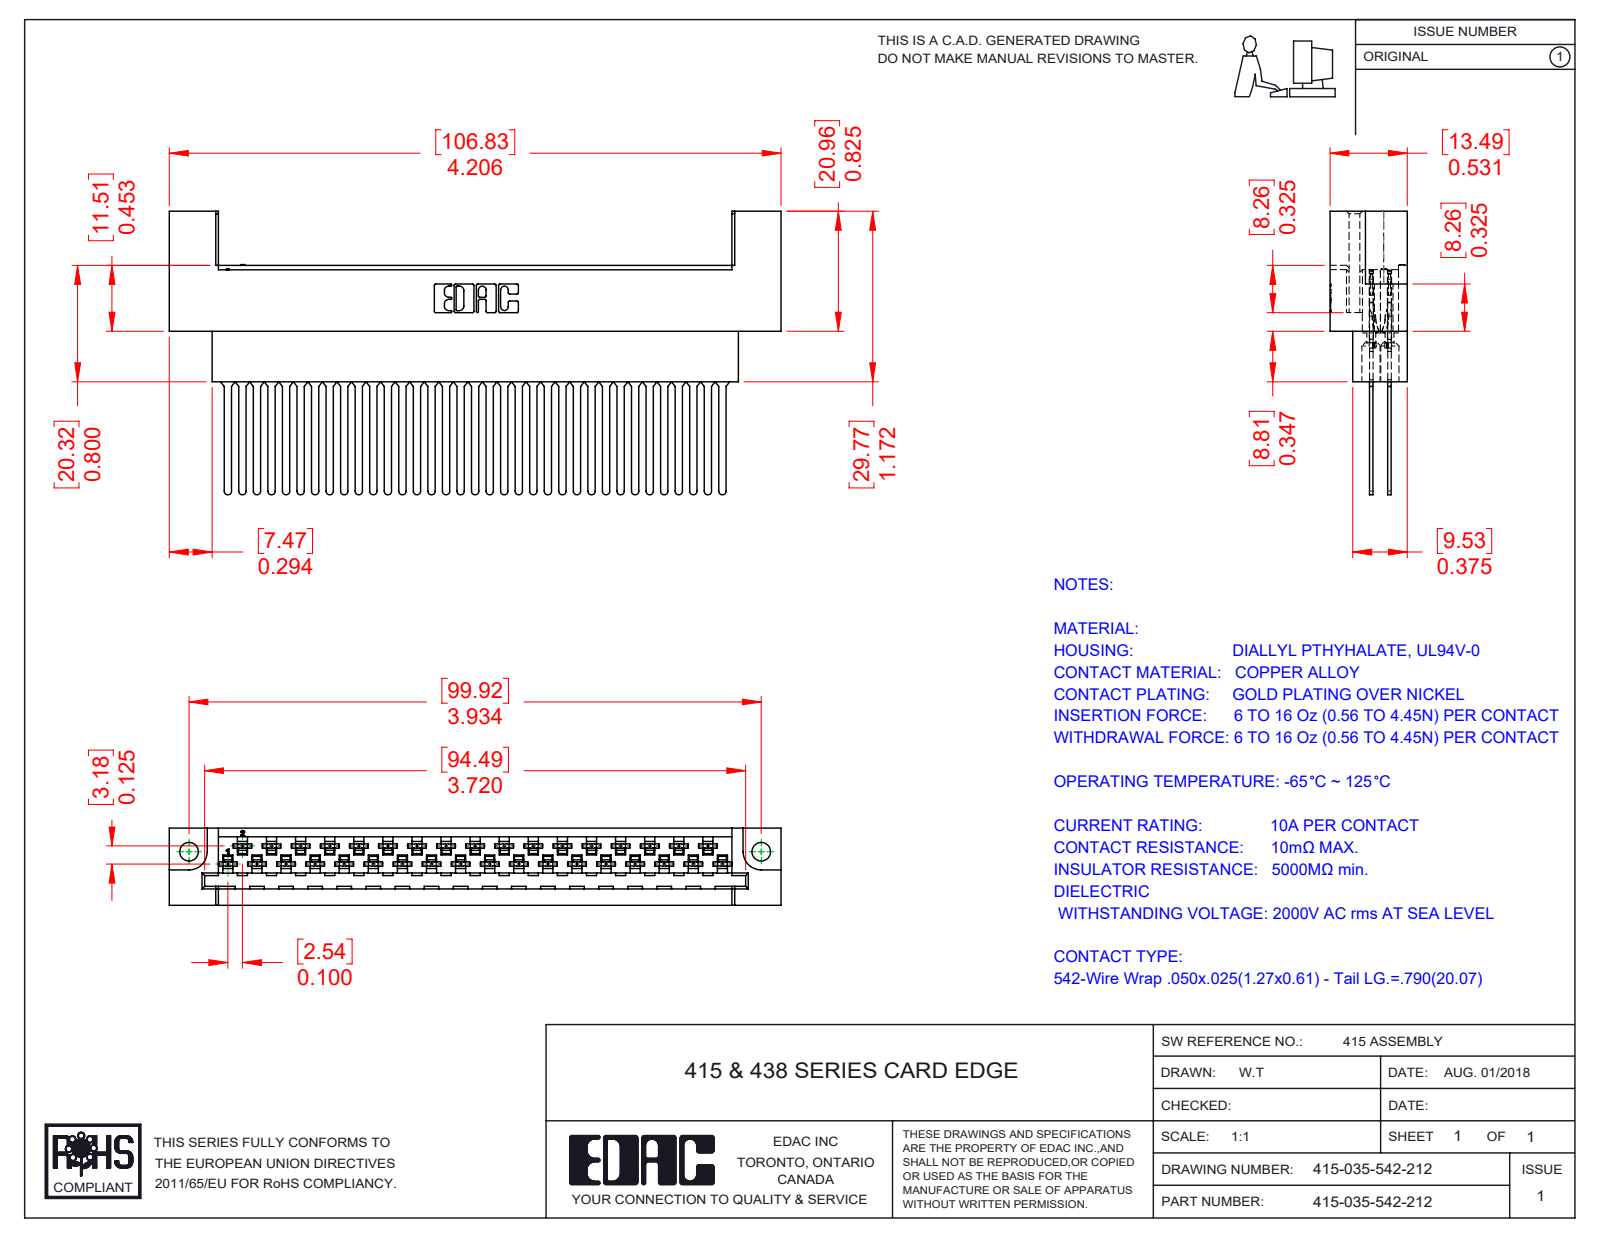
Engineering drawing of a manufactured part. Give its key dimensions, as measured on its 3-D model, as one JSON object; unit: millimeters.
{"part_name": "415-035-542-212; 415-210-001_415-210-035-212; 516-290-001_542", "step_written_by": "SolidWorks 2016 (CONFIG_CONTROL_DESIGN)", "units": "millimeters", "bodies": {"solids": 36, "faces": 3590, "planar": 2297, "cylindrical": 956, "other": 337}, "overall_size": [106.83, 49.49, 13.49], "volume_mm3": 19396, "surface_area_mm2": 25097, "round_holes": [[1.27, 35], [3.3, 35], [3.25, 2]], "partial_cylinders_radius": [[0.3, 140], [0.56, 140], [0.18, 70], [0.2, 70], [0.41, 70], [2.03, 70], [0.64, 35], [0.25, 22]], "face_to_face_distances": [3.18, 0.61, 1.88, 7.49, 13.49, 6.61, 6.88, 6, 1.27, 2.82], "hole_center_spacings": [5.08, 10.16, 15.24, 20.32, 25.4, 30.48, 35.56, 2.54]}
